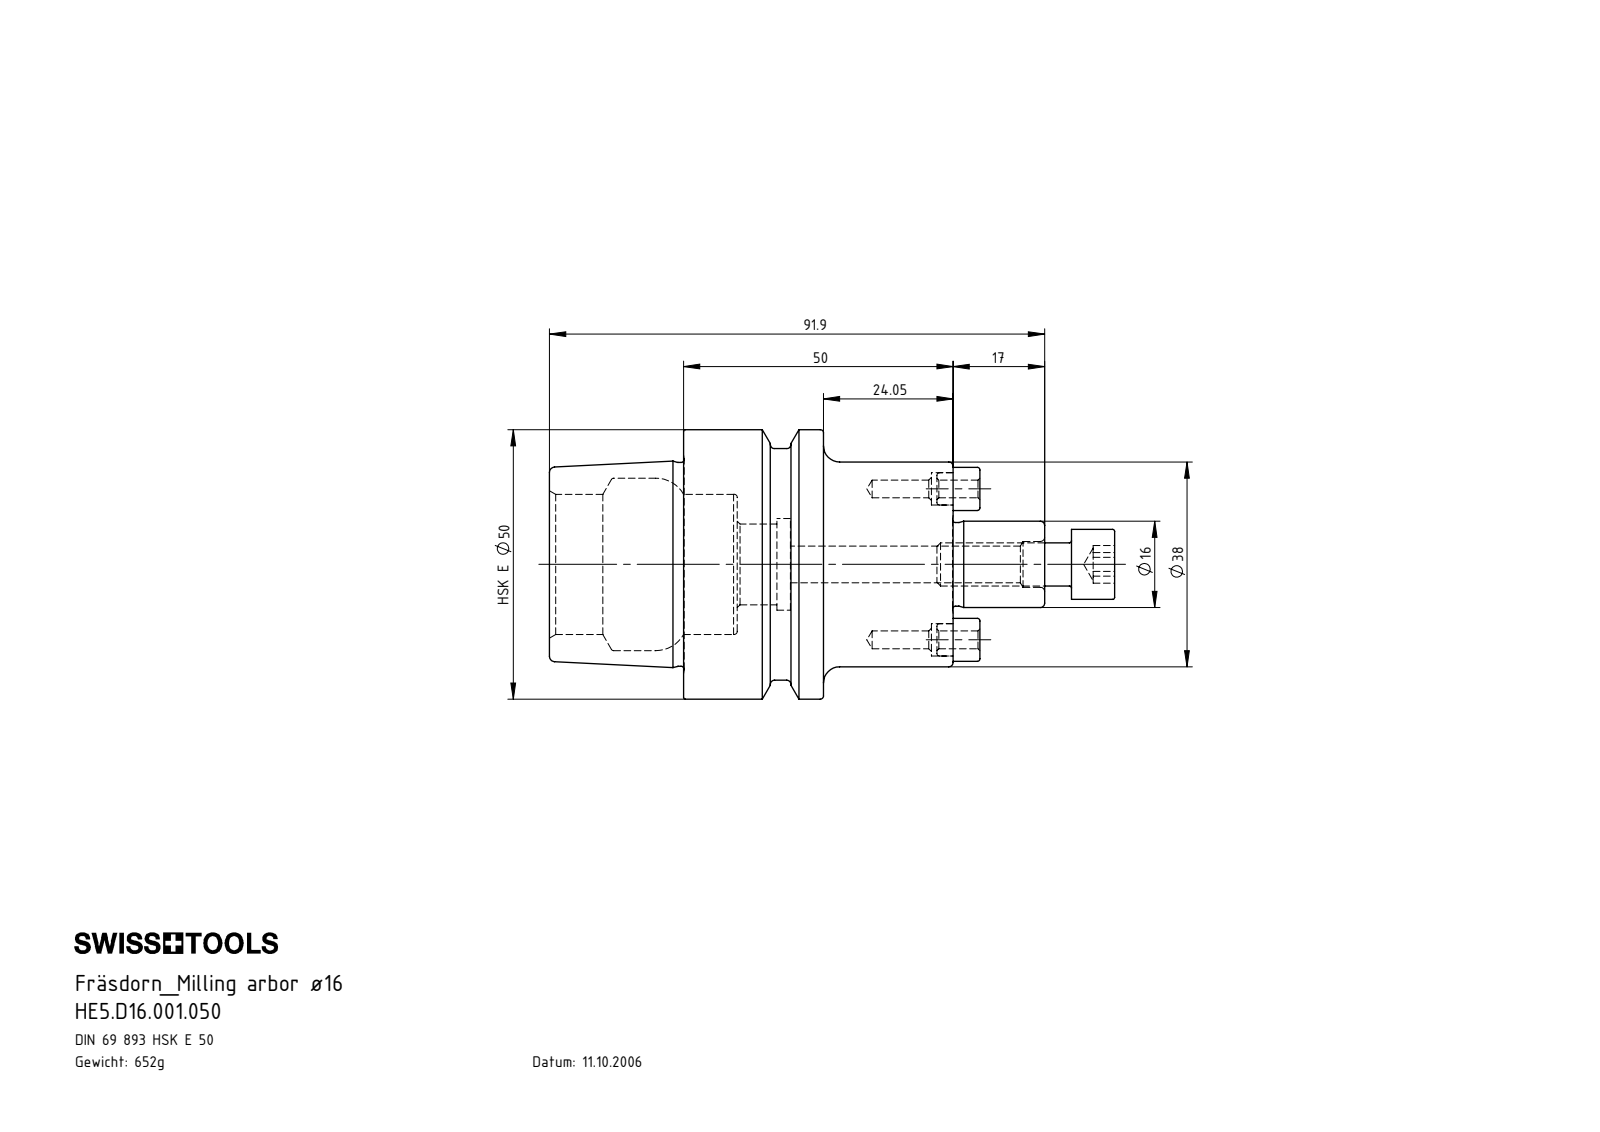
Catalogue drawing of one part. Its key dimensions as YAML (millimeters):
part_name: "D16-ER1.002.025_A_Default; HE5-D16.001.050_A_Fertigbearbeitung; D16-ER2.001.015_A; HE5.D16.001.050"
step_written_by: "SolidWorks 2011 (AUTOMOTIVE_DESIGN)"
units: millimeters
bodies: {solids: 4, faces: 171, planar: 33, cylindrical: 52, other: 86}
overall_size: [104.9, 50, 50]
volume: 83048
surface_area: 21839
round_holes:
  - {diameter: 3.3, count: 2}
  - {diameter: 6, count: 2}
  - {diameter: 6.8, count: 1}
  - {diameter: 8.5, count: 1}
  - {diameter: 15, count: 1}
  - {diameter: 17, count: 1}
  - {diameter: 26, count: 1}
  - {diameter: 32, count: 1}
round_bosses_or_shafts:
  - {diameter: 8, count: 3}
  - {diameter: 50, count: 1}
  - {diameter: 42.95, count: 1}
  - {diameter: 38, count: 1}
  - {diameter: 37.81, count: 1}
  - {diameter: 16, count: 1}
  - {diameter: 15.5, count: 1}
  - {diameter: 13, count: 1}
face_to_face_distances: [50, 25.95, 24.05, 24.9, 50.85, 74.9, 34.85, 9.95, 16, 40.05]
hole_center_spacings: [14, 28]
